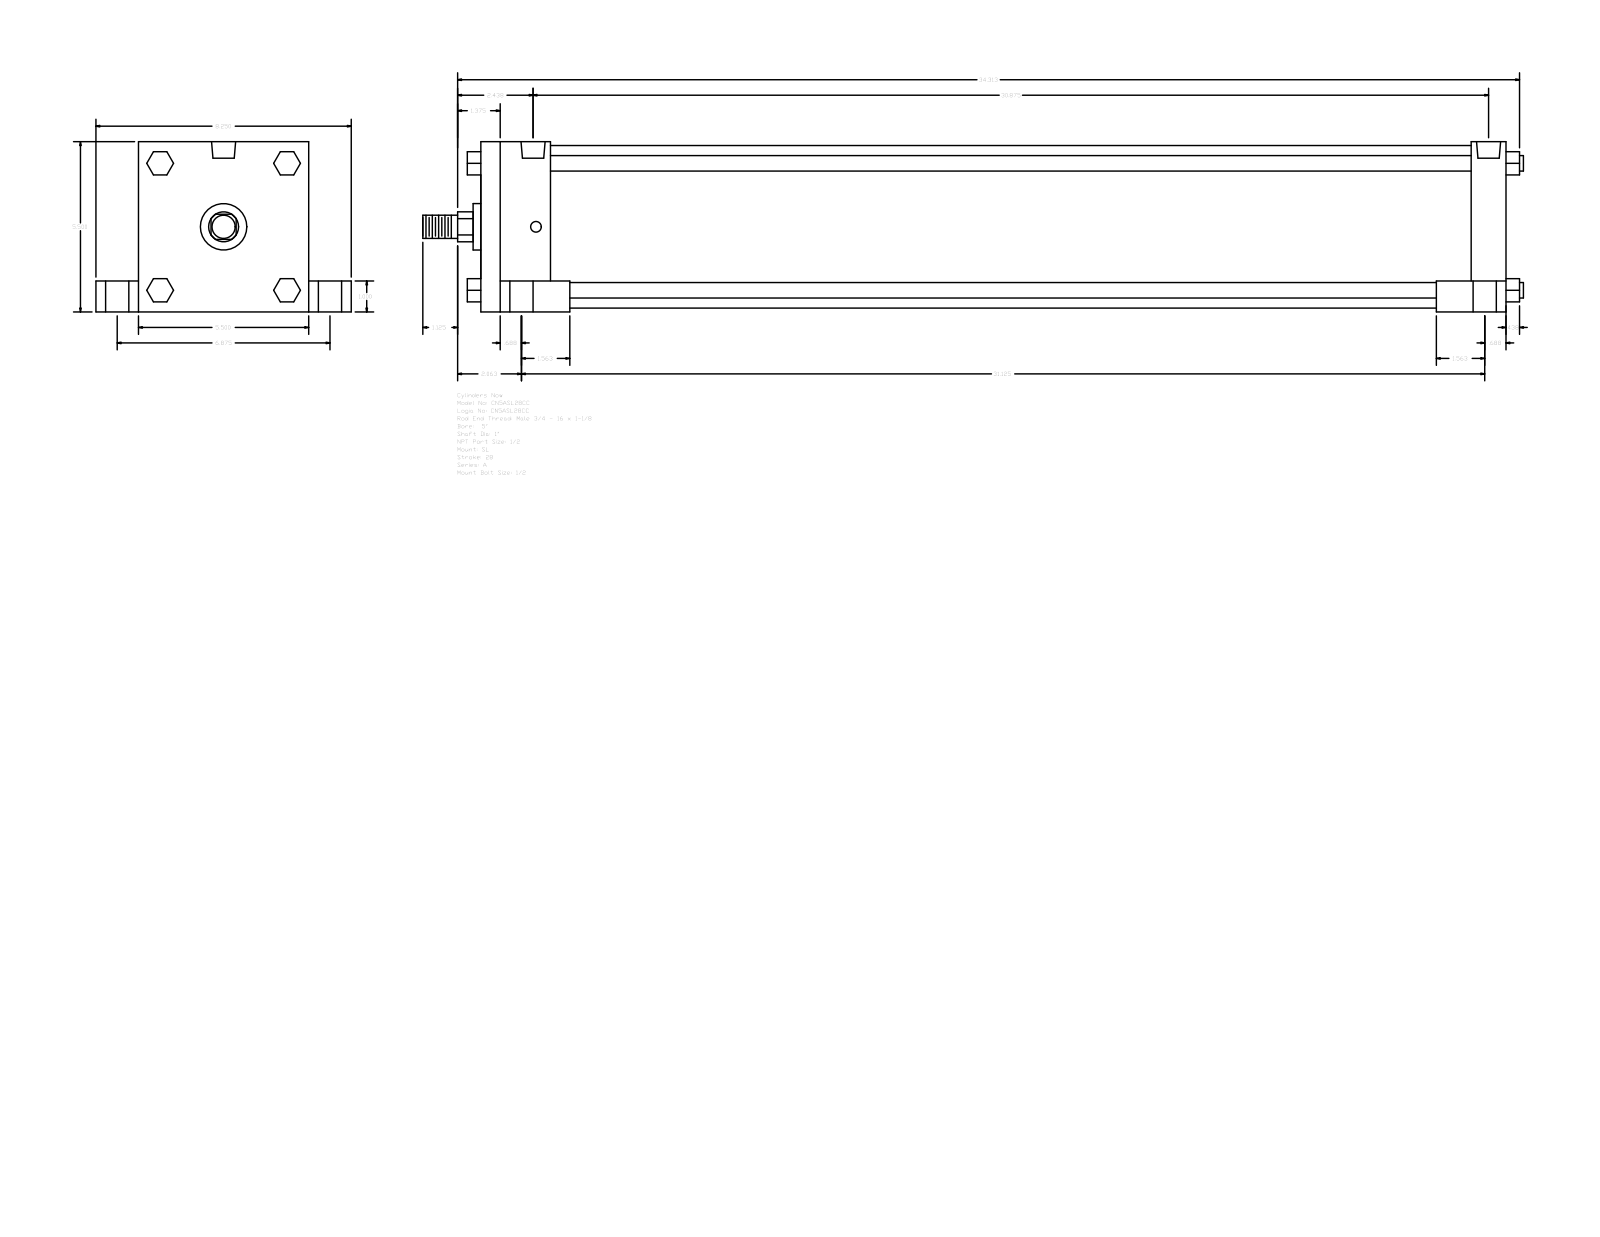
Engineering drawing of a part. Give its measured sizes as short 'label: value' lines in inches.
name: A_SL__0500_1
written by: GSSL Pune (CONFIG_CONTROL_DESIGN)
unit: in
bodies: 0 solids, 150 faces (114 planar, 36 cylindrical, 0 other)
size: 35.563 × 8.25 × 5.5
holes: 4× ⌀0.344, 4× ⌀0.75, 4× ⌀1, 2× ⌀0.778
bosses: 4× ⌀0.5, 1× ⌀5.25, 1× ⌀1.5, 1× ⌀1, 1× ⌀0.75
rounds: 1× R0.484
face distances: 5.5, 33.125, 2.25, 30.875, 1, 4.5, 1.375, 6.875, 1.125, 32
hole spacings: 0.094, 3.437, 3.44, 3.458, 3.469, 6.875, 30.687, 30.781
